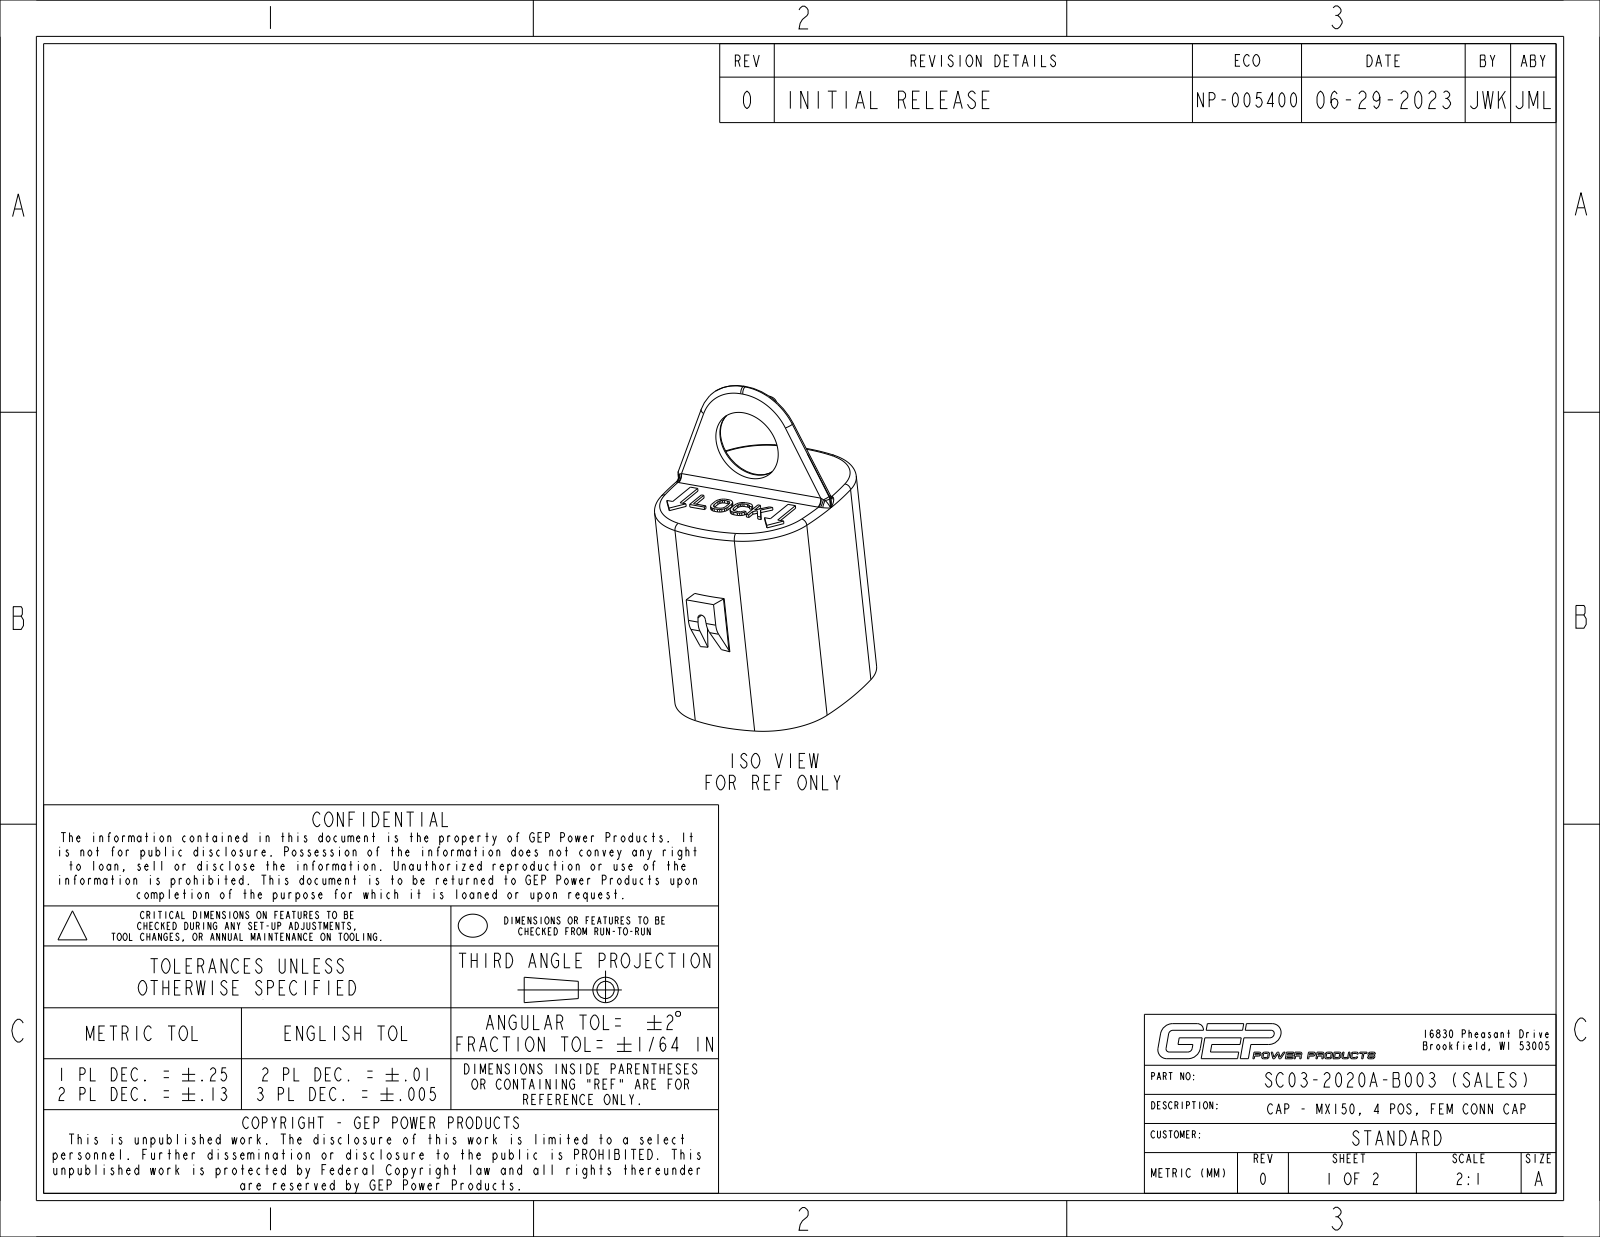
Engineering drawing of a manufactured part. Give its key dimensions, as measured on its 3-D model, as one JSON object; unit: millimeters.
{"part_name": "PC03-2020A-B003_NCF; SC03-2020A-B003_NCF_ASM", "step_written_by": "CREO PARAMETRIC BY PTC INC, 2017110 (CONFIG_CONTROL_DESIGN)", "units": "millimeters", "bodies": {"solids": 1, "faces": 439, "planar": 236, "cylindrical": 33, "other": 170}, "overall_size": [29, 19.47, 15.44], "volume_mm3": 1537, "surface_area_mm2": 2573, "round_holes": [[3, 1], [6.35, 1]], "partial_cylinders_radius": [[5.72, 4], [0.5, 3], [0.3, 2], [0.6, 2], [14.23, 2], [31.73, 2], [0.38, 1], [2, 1]], "face_to_face_distances": [1, 18, 19, 18.15, 0.85, 19.25, 1.25, 1.1, 18.25, 0.75]}
